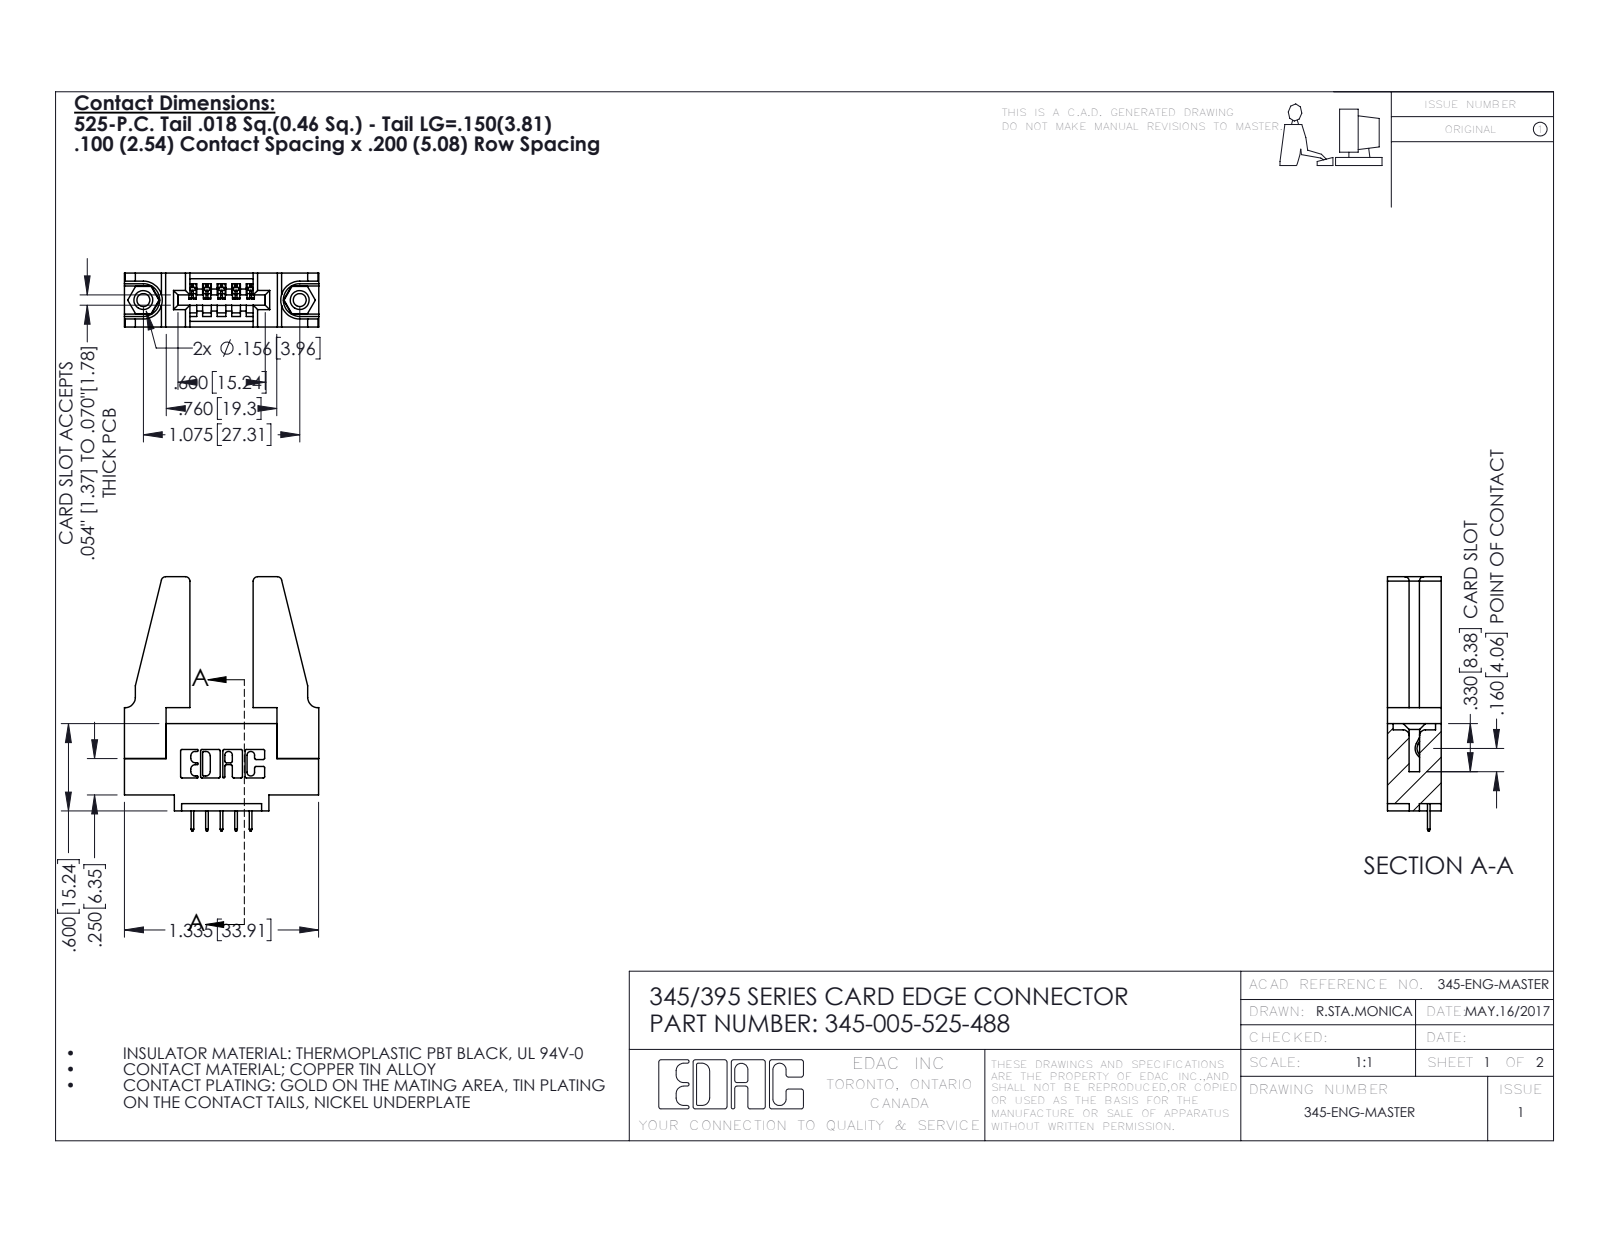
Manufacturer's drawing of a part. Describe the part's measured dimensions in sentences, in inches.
The part is named "345-250-001_345-250-001-102; 345-292-001_345-293-125; 345 Part_0.110 Offset - 0.156 Dia-TH; 345-005-525-488 (+1 more)". Its 3-D file was written by "SolidWorks 2020 (CONFIG_CONTROL_DESIGN)". It is 10 solids with 564 faces: 386 planar, 162 cylindrical and 16 other. Overall it measures 1.747 by 1.336 by 0.37 inches. Its volume is 0.371 cubic inches and its surface area 9.914 square inches. Round holes: 2 of diameter 0.089, 2 of diameter 0.125, 2 of diameter 0.156, 1 of diameter 0.064. Round bosses or shafts: 2 of diameter 0.155. Partial cylindrical surfaces (rounded edges, fillets, slot ends): 22 of radius 0.01, 10 of radius 0.006, 8 of radius 0.03, 6 of radius 0.007, 6 of radius 0.031, 3 of radius 0.026, 2 of radius 0.031, 2 of radius 0.04. The main face-to-face distances are 0.37, 0.072, 0.298, 0.2, 0.148, 0.15, 0.22, 0.077, 0.45, 0.287. The hole center spacings are 0.27, 0.847, 1.075.
